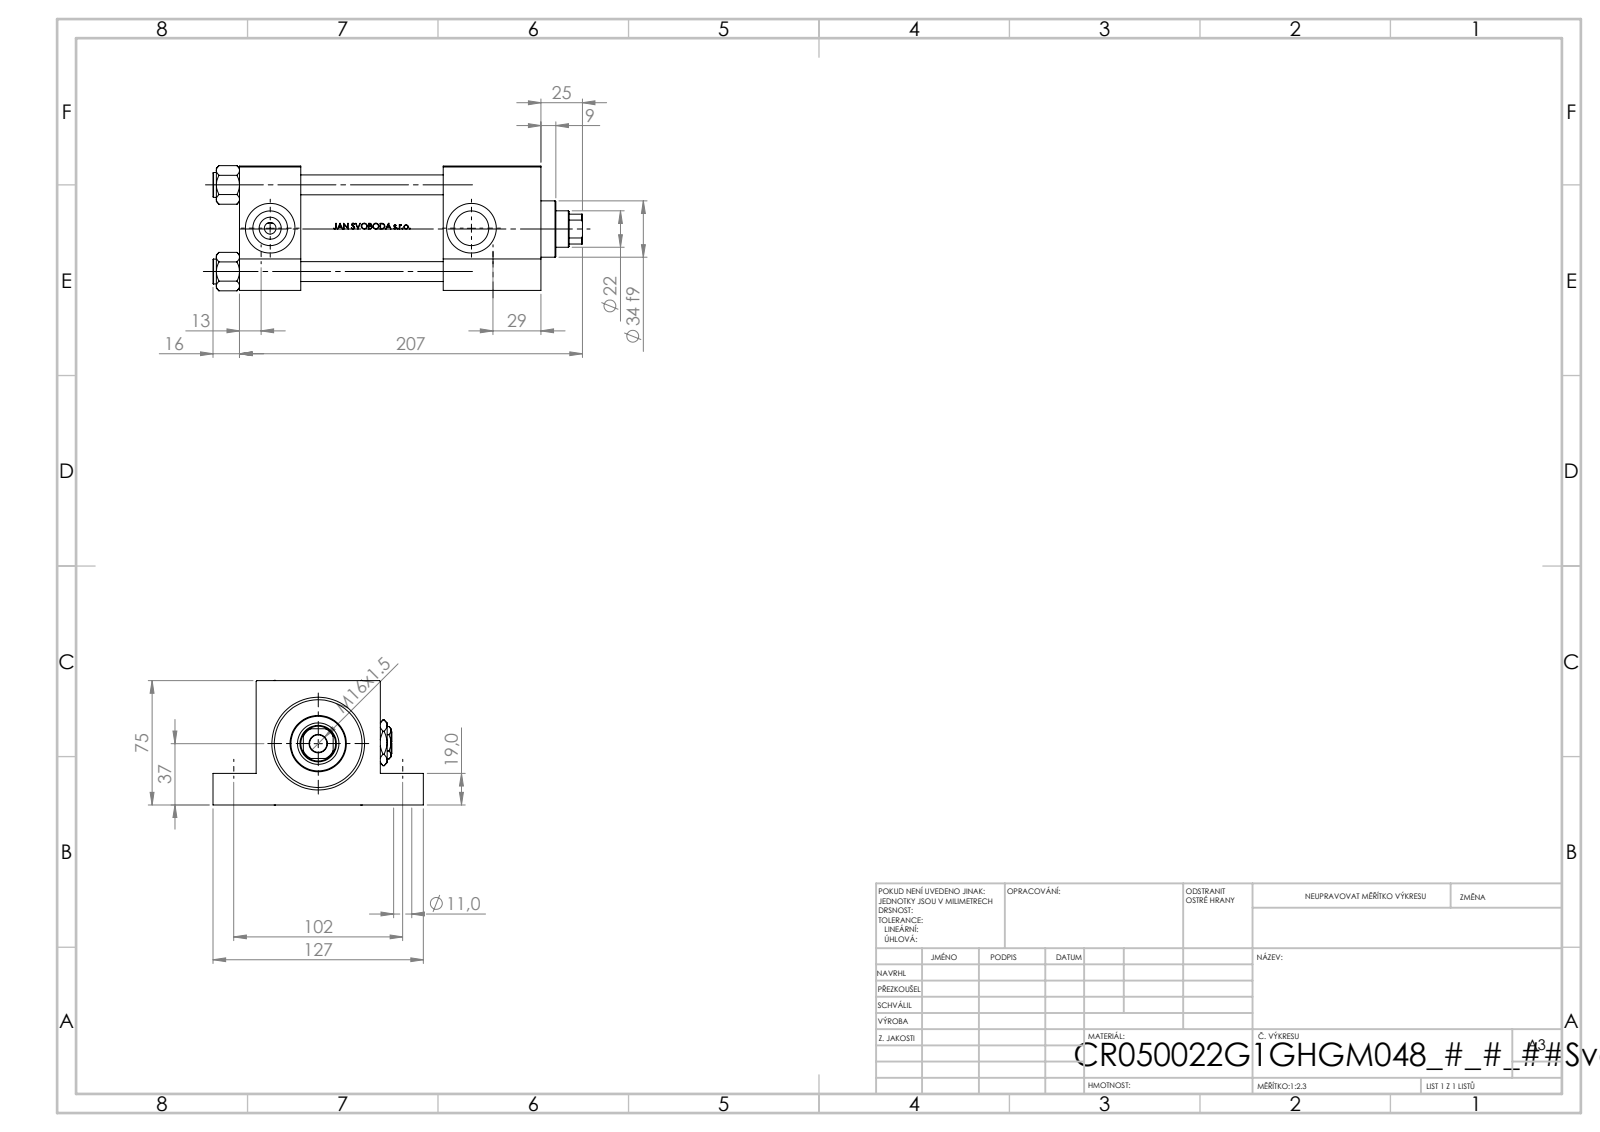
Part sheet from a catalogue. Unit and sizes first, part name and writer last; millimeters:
Units: millimetres
Overall size (bounding box): 223 × 127 × 75.54
Round holes (diameter × count): ⌀11 ×4, ⌀12 ×4, ⌀7 ×2, ⌀20.96 ×2, ⌀30 ×2, ⌀10.5 ×1, ⌀22 ×1, ⌀25 ×1, ⌀41 ×1, ⌀50 ×1, ⌀53 ×1
Round bosses / shafts (diameter × count): ⌀15 ×4, ⌀56 ×1, ⌀34 ×1
Partial cylindrical surfaces — rounded edges, fillets, slot ends (radius × count): R10.5 ×1
Main face-to-face distances: 75, 37, 182, 145, 19, 56, 123, 86, 59, 26
Hole centre spacings: 52.3, 36.63, 37.34, 73.96, 102, 140, 173.22, 121.5
Volume: 789 700 mm³ · Surface area: 176 785 mm²
Bodies: 12 solids, 1134 faces (454 planar, 128 cylindrical, 552 other)
Part name (STEP PRODUCT): Zatka_pro_OIL_PORT; NUT_M5_G; V215CR_G_TYCINKA; V215CR_G_Body (+2 more)
STEP written by: SolidWorks 2019 (CONFIG_CONTROL_DESIGN)
